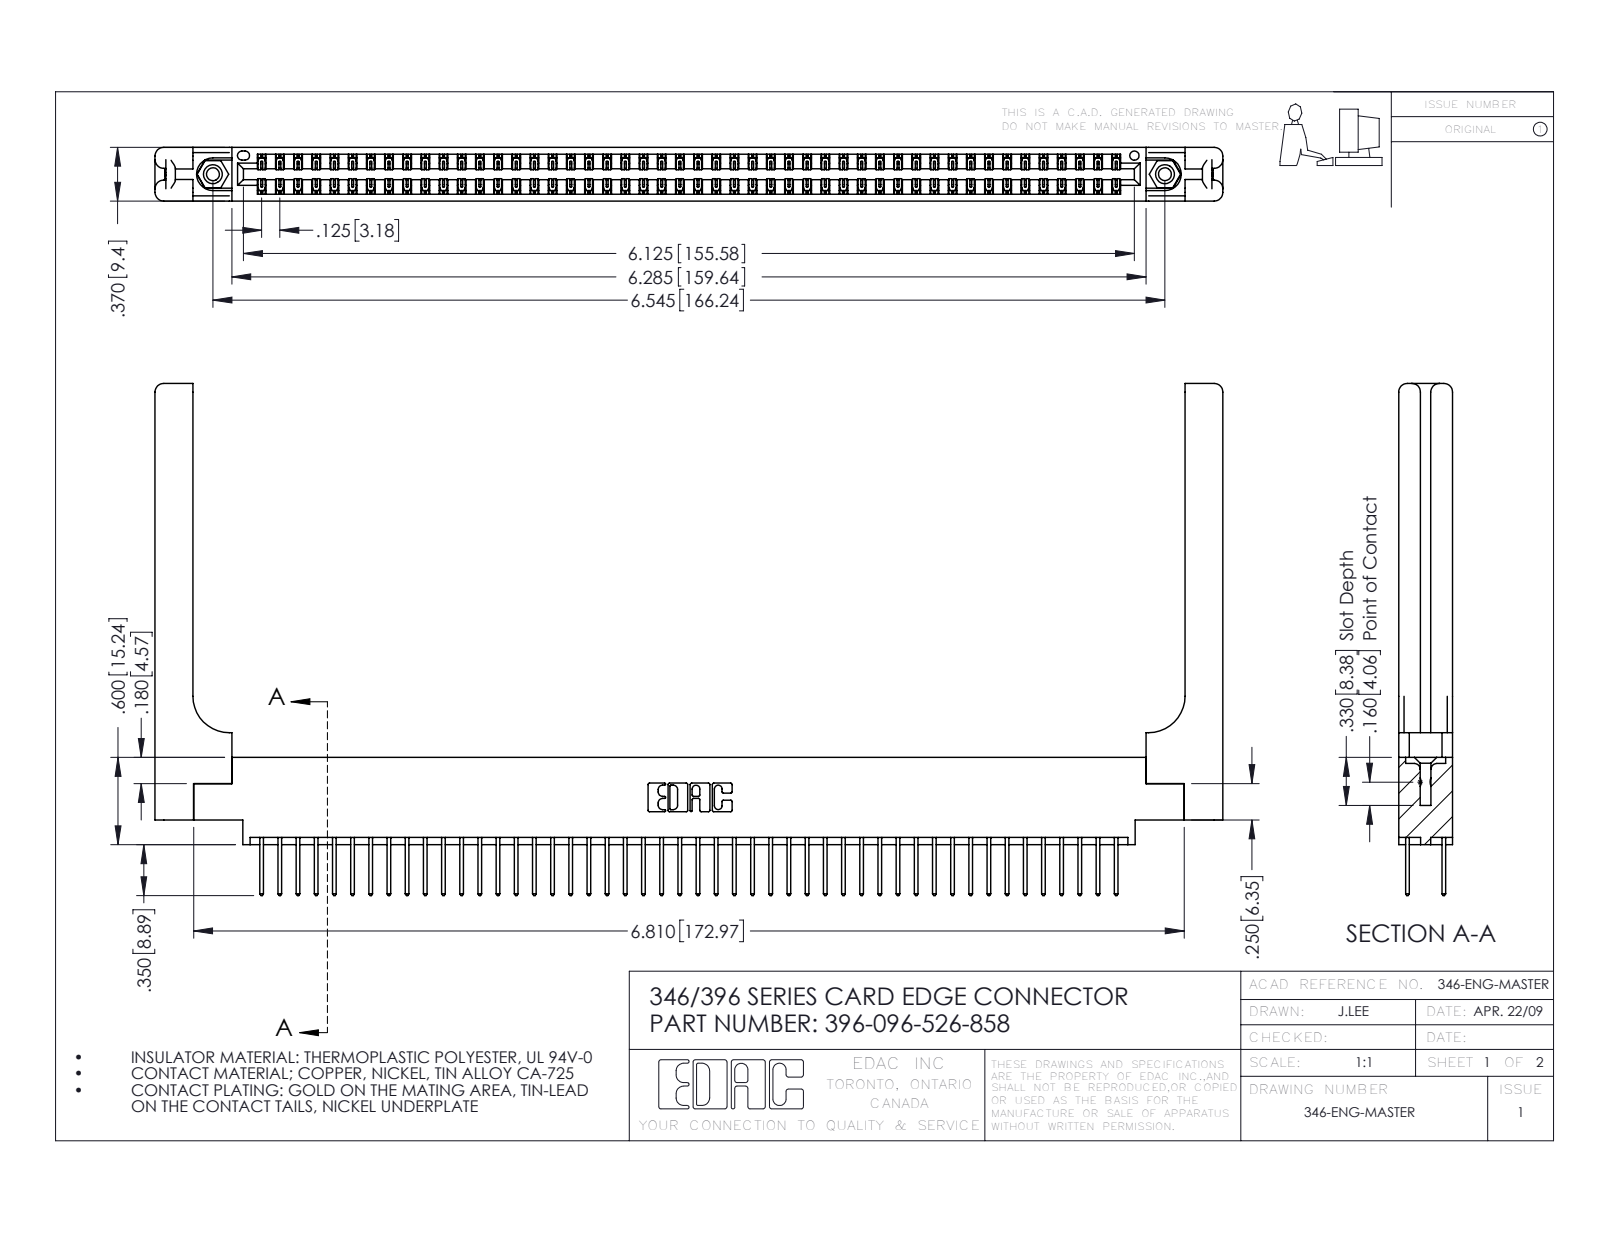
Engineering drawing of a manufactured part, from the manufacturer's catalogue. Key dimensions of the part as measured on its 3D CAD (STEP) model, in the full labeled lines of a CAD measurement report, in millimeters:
Part name (STEP PRODUCT): 346 Part_0.170 Offset - 0.156 Dia-TH; 345-250-001_345-250-001-102; 346-220-058_345-220-058; 396-096-526-858 (+1 more)
STEP written by: SolidWorks 2016 (CONFIG_CONTROL_DESIGN)
Units: millimetres
Bodies: 101 solids, 5374 faces (3588 planar, 1726 cylindrical, 60 other)
Overall size (bounding box): 186.5 × 89.4 × 9.4
Volume: 25 730 mm³ · Surface area: 31 010 mm²
Round holes (diameter × count): ⌀2.3 ×2, ⌀3.2 ×2, ⌀4 ×2, ⌀1.6 ×1
Round bosses / shafts (diameter × count): ⌀3.9 ×2
Partial cylindrical surfaces — rounded edges, fillets, slot ends (radius × count): R0.2 ×144, R0.3 ×96, R0.3 ×22, R1.5 ×16, R0.2 ×6, R0.8 ×6, R0.7 ×3, R0.4 ×2
Main face-to-face distances: 1.2, 8.2, 9.4, 1.8, 6.4, 0.6, 7.6, 3.8, 3.8, 7
Hole centre spacings: 6.2, 160.9, 166.2
